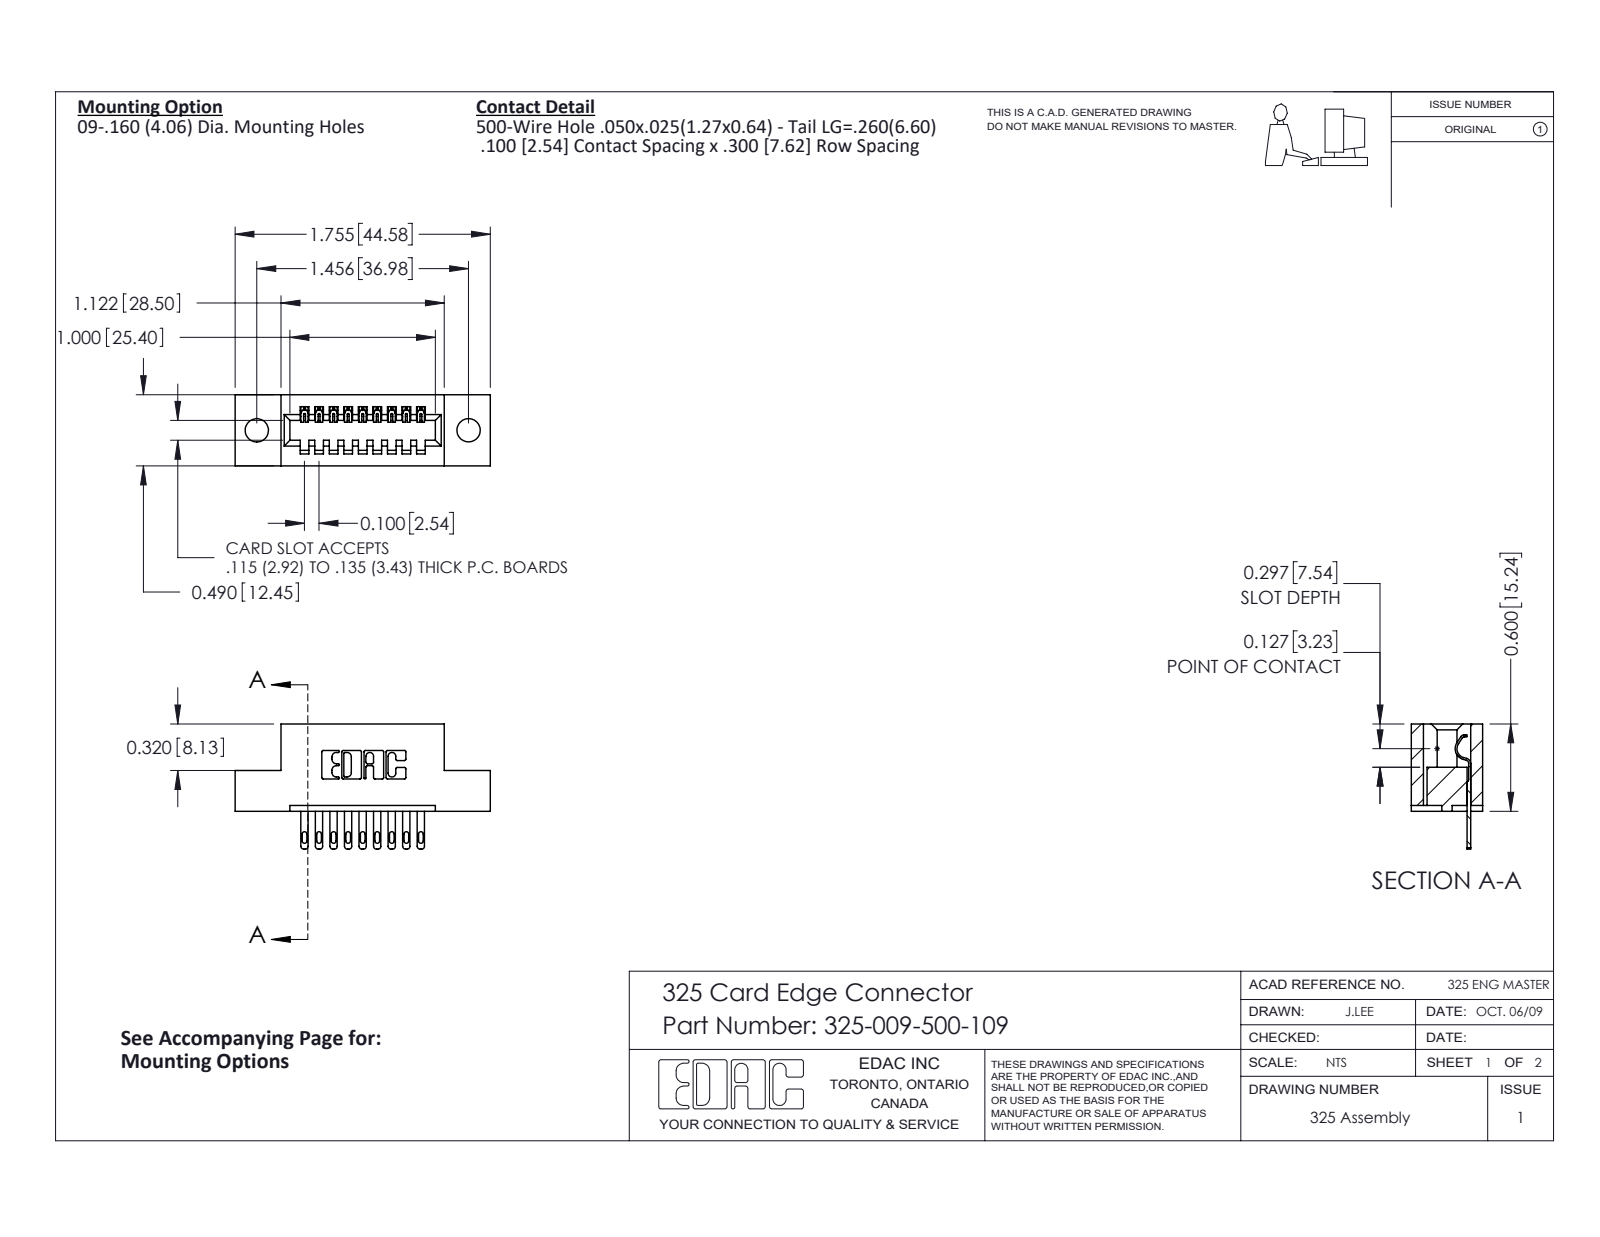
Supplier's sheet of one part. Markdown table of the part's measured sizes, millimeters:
| quantity | value |
| --- | --- |
| part name | 325 Part_.160 TH; 325-009-500-109; 325-292-001_325-293-100 |
| STEP written by | SolidWorks 2016 (CONFIG_CONTROL_DESIGN) |
| units | millimeters |
| bodies | 10 solids, 600 faces (394 planar, 206 cylindrical, 0 other) |
| overall size | 44.6 × 21.8 × 12.4 |
| volume | 5 180 mm³ |
| surface area | 5 010 mm² |
| round holes (diameter × count) | 4.1 × 2 |
| partial cylindrical surfaces (radius × count) | 0.3 × 22, 0.2 × 18, 0.4 × 18, 0.5 × 18, 0.2 × 6, 0.8 × 6, 0.7 × 3, 0.4 × 1 |
| main face-to-face distances | 7.6, 1, 2.1, 10.3, 2.5, 12.4, 5.1, 15.2, 10.2, 1.5 |
| hole center spacings | 37 |
